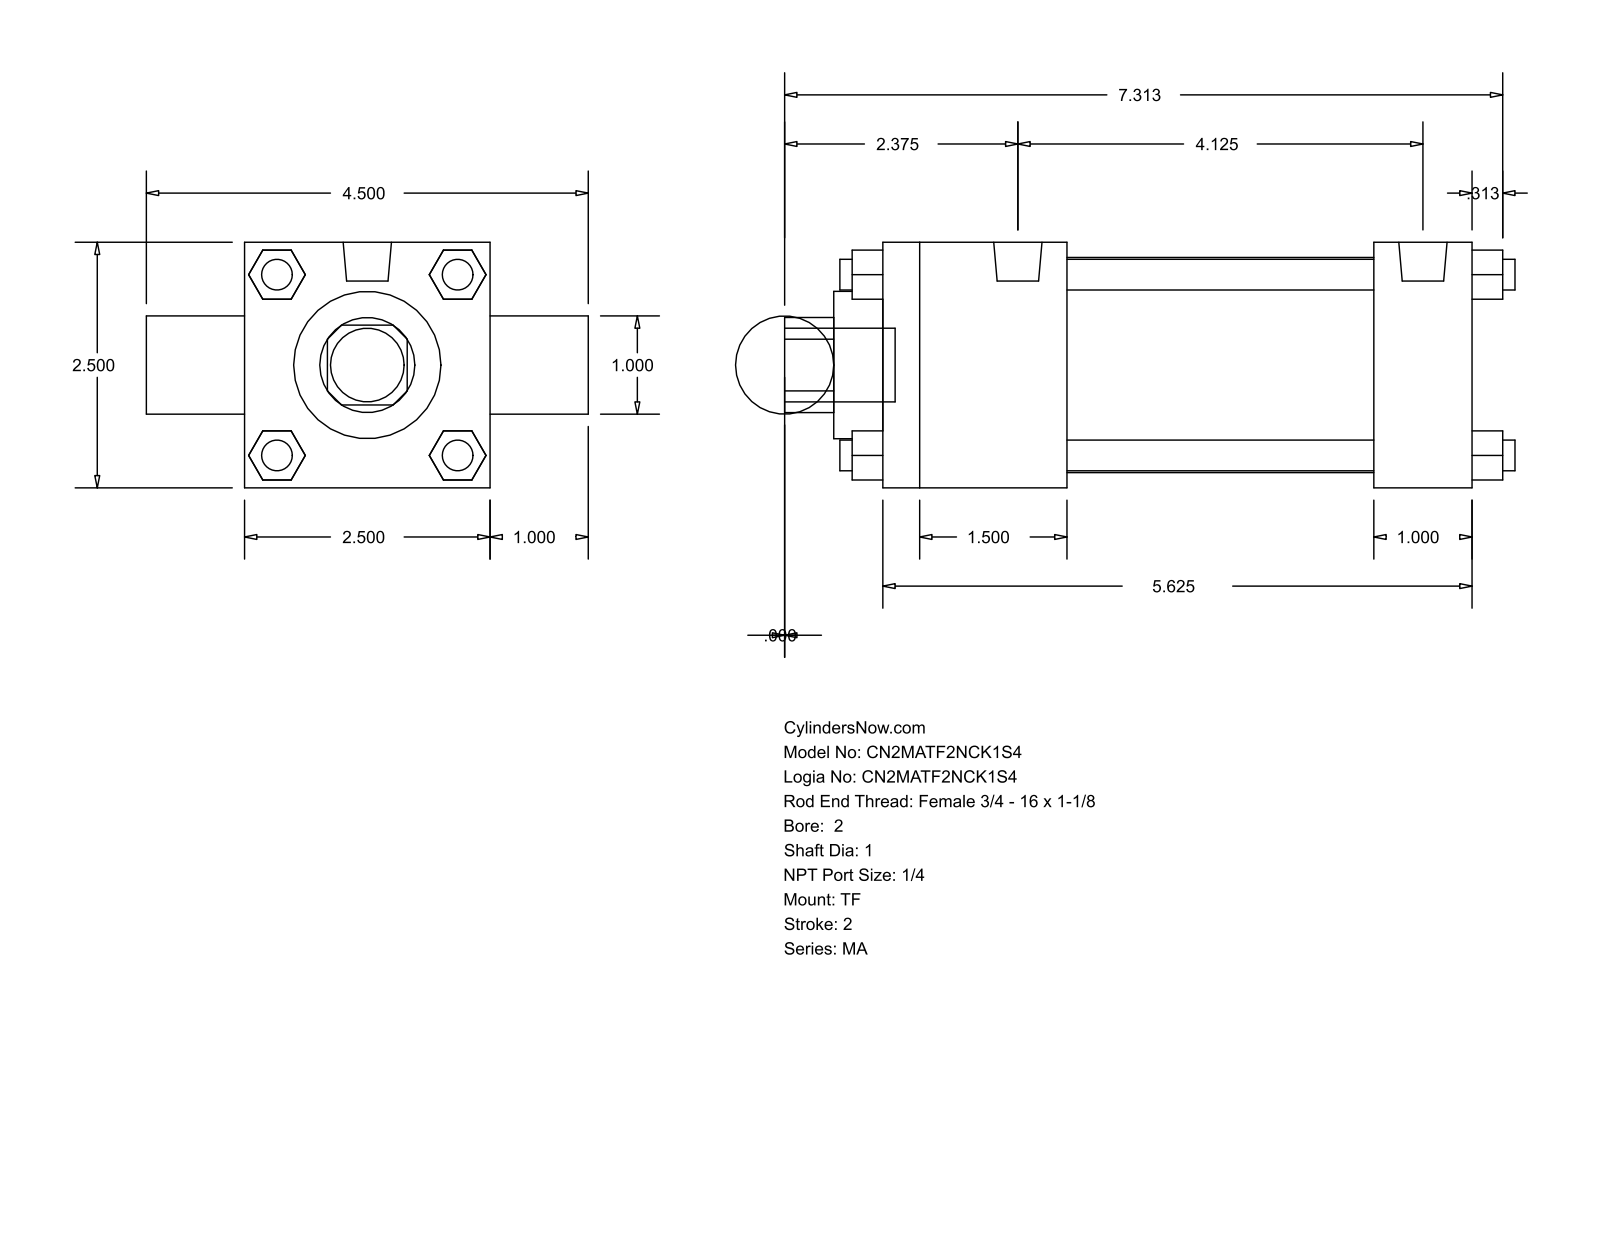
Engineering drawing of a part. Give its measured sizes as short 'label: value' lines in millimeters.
name: MA_TF__0200_1
written by: GSSL Pune (CONFIG_CONTROL_DESIGN)
unit: mm
bodies: 0 solids, 120 faces (92 planar, 28 cylindrical, 0 other)
size: 188.91 × 114.3 × 63.5
holes: 2× ⌀25.4, 1× ⌀38.1, 1× ⌀55.63
bosses: 7× ⌀7.94, 2× ⌀12.49, 1× ⌀19.05
rounds: 1× R12.29
face distances: 63.5, 25.4, 152.4, 12.7, 47.63, 127, 79.37, 104.77, 88.9, 23.37
